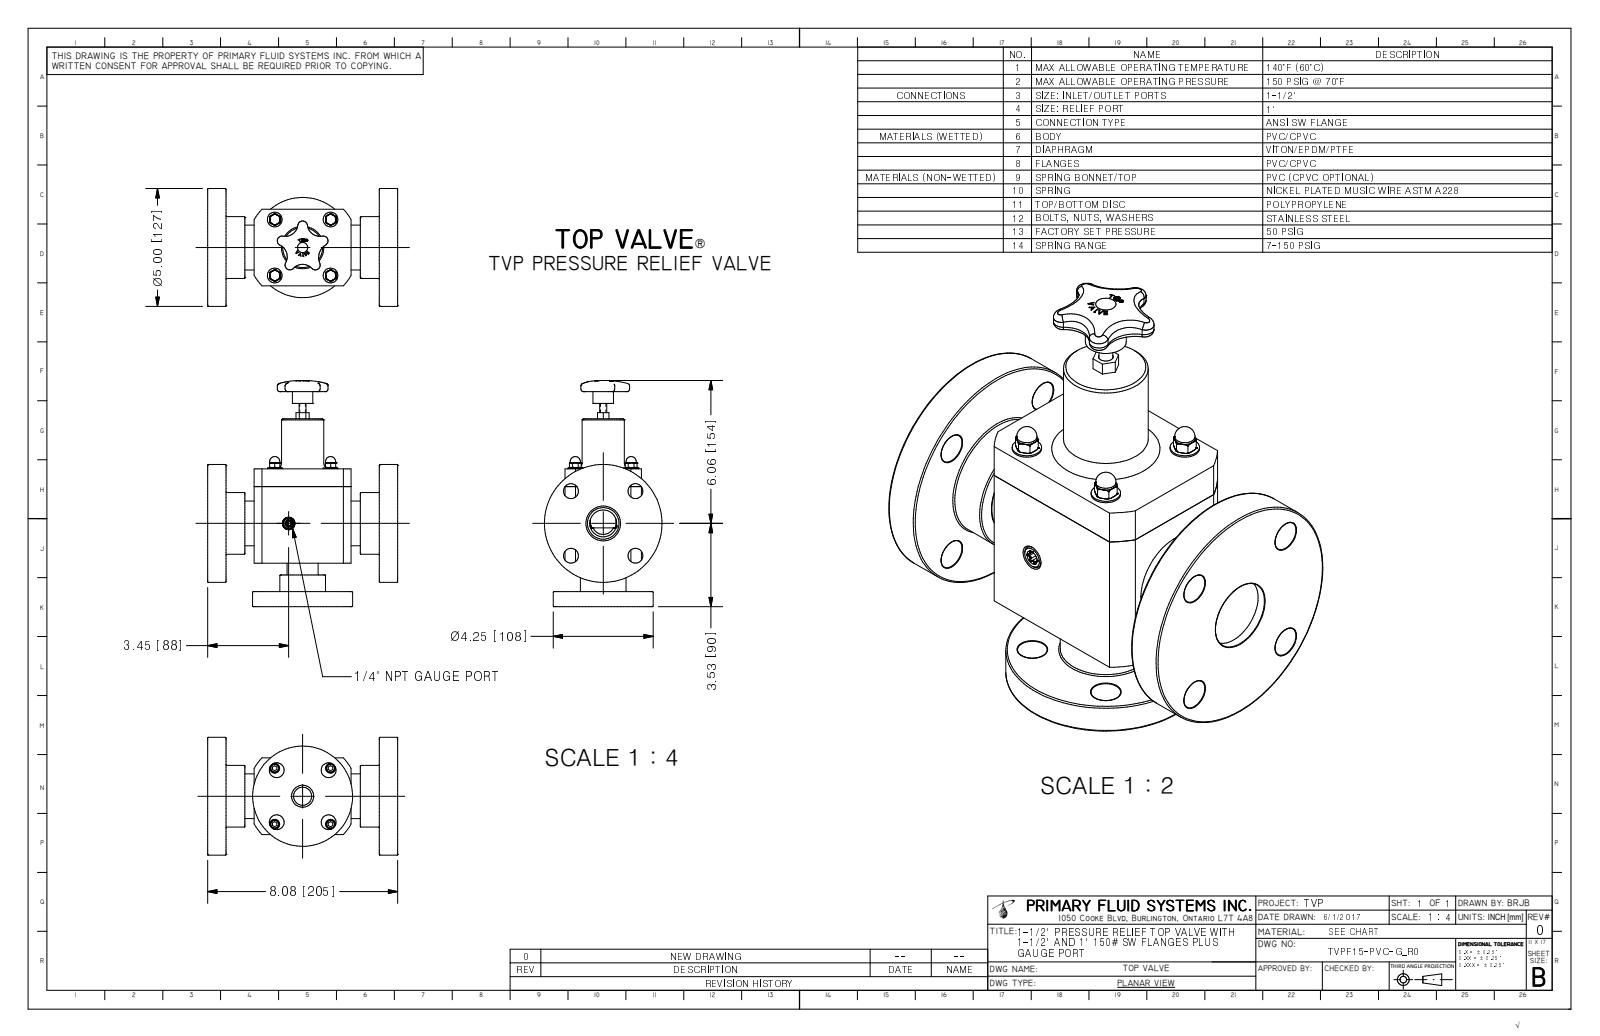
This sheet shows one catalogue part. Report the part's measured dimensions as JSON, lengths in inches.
{"part_name": "TVPF15-PVC-G_R0", "step_written_by": "Autodesk Inventor 2009 (AUTOMOTIVE_DESIGN)", "units": "inches", "bodies": {"solids": 1, "faces": 446, "planar": 165, "cylindrical": 76, "other": 205}, "overall_size": [9.593, 8.08, 5], "volume_in3": 97.73, "surface_area_in2": 342.5, "round_holes": [[0.63, 8], [0.175, 4], [0.936, 1], [0.957, 1], [1.476, 1], [1.5, 1]], "round_bosses_or_shafts": [[0.625, 4], [0.433, 4], [0.375, 4], [5, 1], [4.25, 1], [2.62, 1], [1.941, 1], [1.9, 1]], "partial_cylinders_radius": [[0.027, 6], [0.085, 5], [0.205, 5], [0.536, 4], [0.656, 4], [0.625, 1], [0.745, 1], [2.375, 1]], "face_to_face_distances": [0.78, 7.3, 8.08, 3.25, 1.978, 6.103, 1.197, 5.322, 6.52, 1.843], "hole_center_spacings": [1.562, 1.937, 2.209, 2.294, 2.74, 0.117, 0.117, 1.679]}
